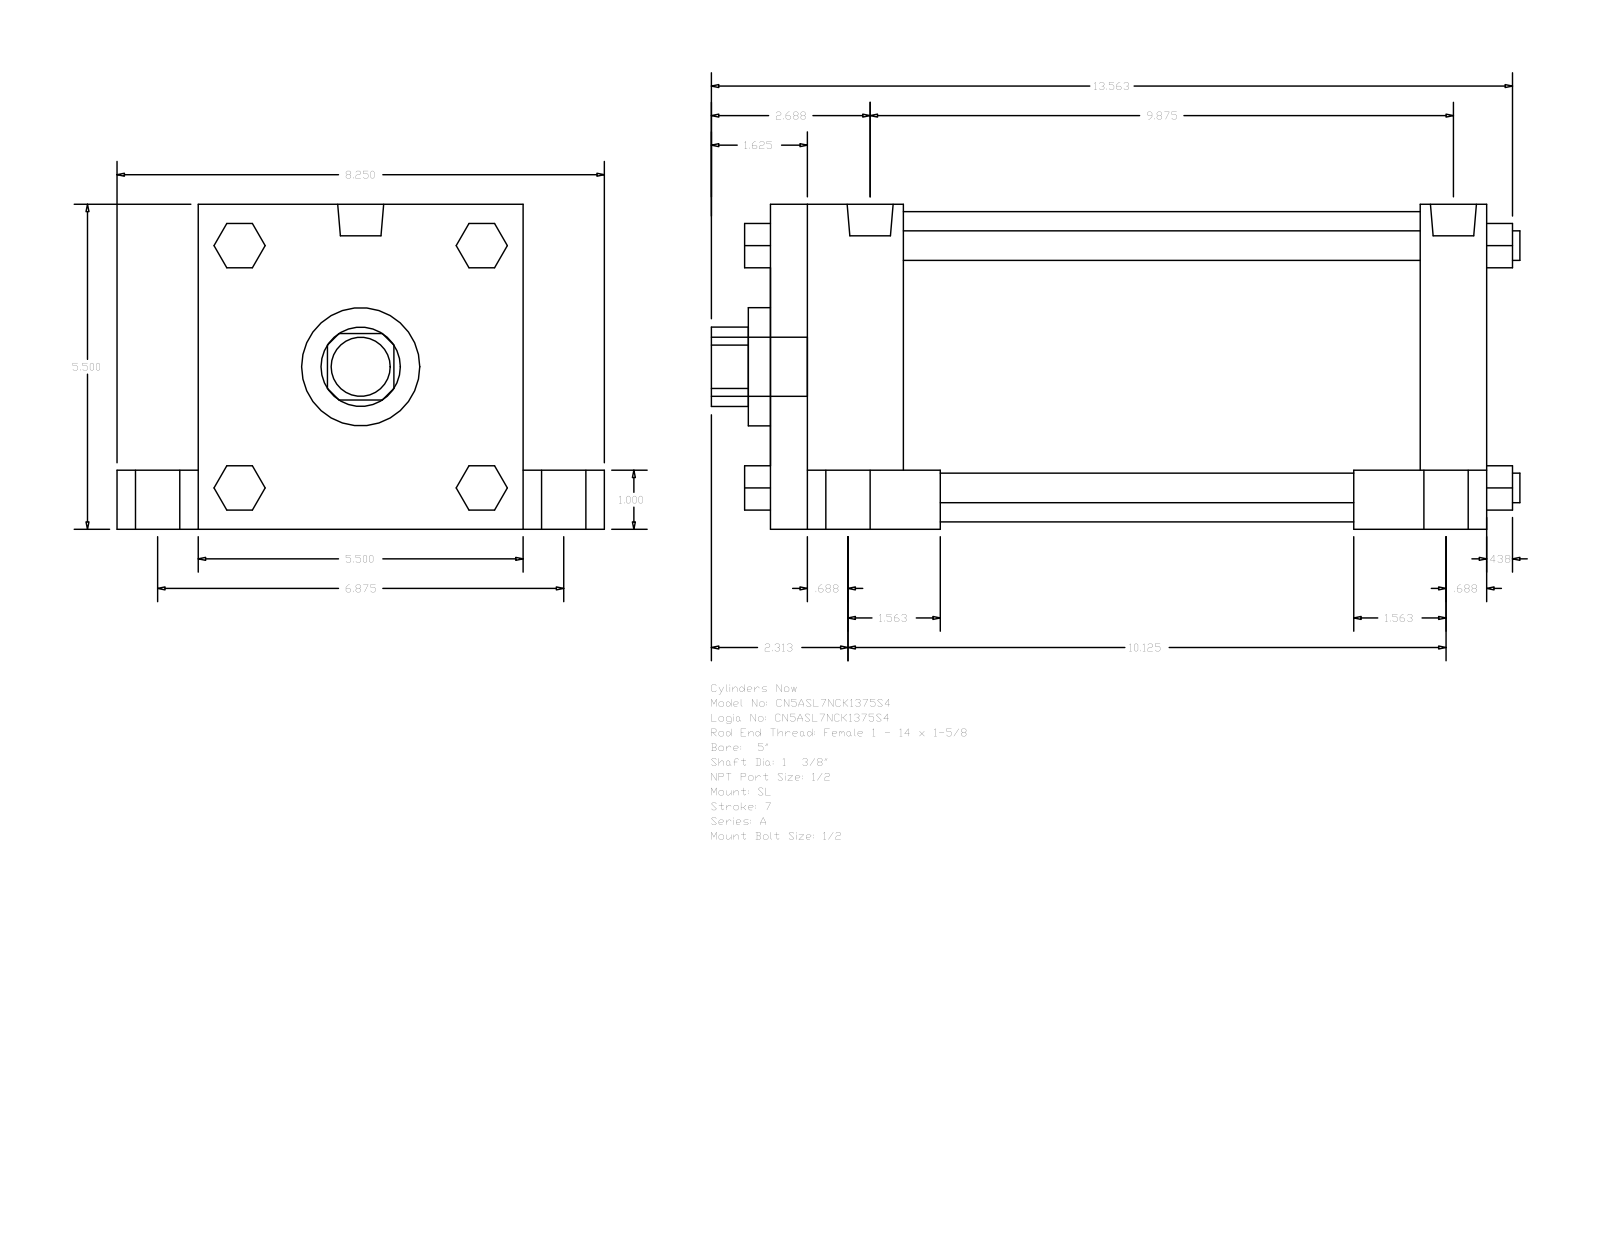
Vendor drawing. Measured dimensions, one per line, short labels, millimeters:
name: A_SL__0500_1.375
written by: GSSL Pune (CONFIG_CONTROL_DESIGN)
unit: mm
bodies: 0 solids, 150 faces (114 planar, 36 cylindrical, 0 other)
size: 347.66 × 209.55 × 139.7
holes: 1× ⌀34.92, 1× ⌀50.8, 1× ⌀133.35
bosses: 5× ⌀25.4, 4× ⌀19.05, 4× ⌀12.7, 4× ⌀8.73, 2× ⌀19.77
rounds: 1× R17.06
face distances: 139.7, 307.98, 57.15, 250.83, 25.4, 114.3, 34.93, 174.63, 28.58, 279.4
